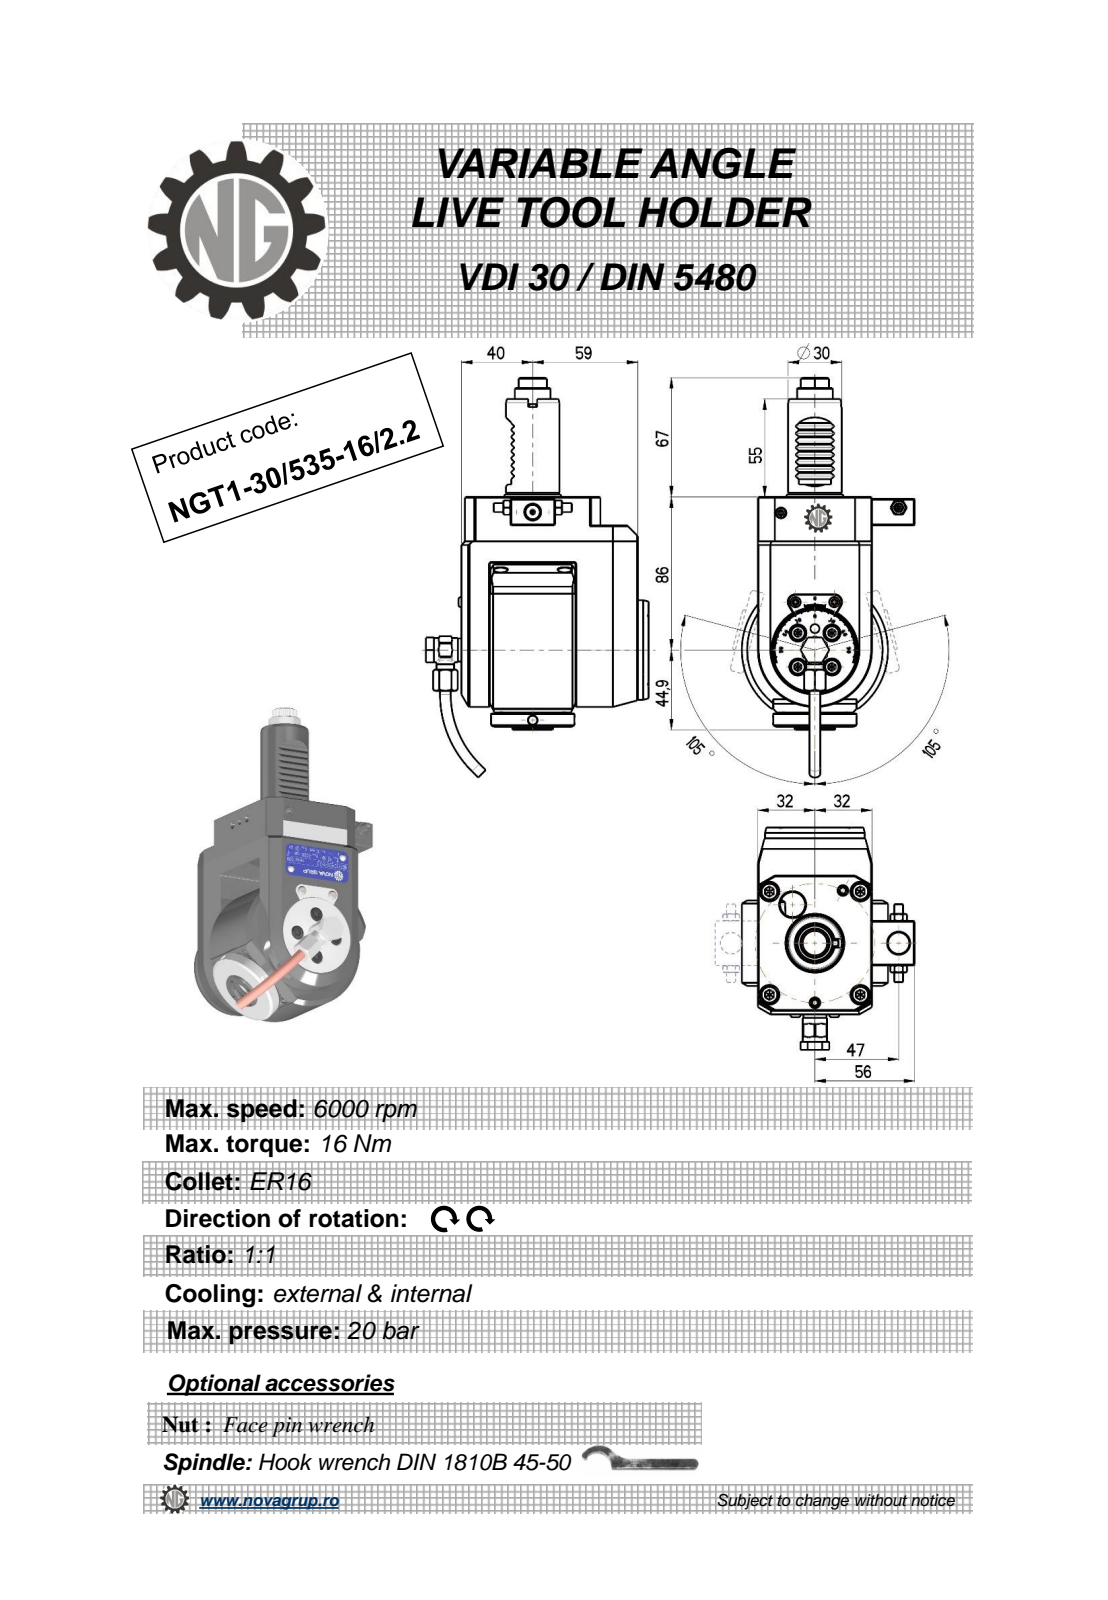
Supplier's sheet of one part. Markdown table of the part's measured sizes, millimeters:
| quantity | value |
| --- | --- |
| part name | NGT1_30_531_16_2_2 |
| STEP written by | PRO/ENGINEER BY PARAMETRIC TECHNOLOGY CORPORATION, 2010280 (CONFIG_CONTROL_DESIGN) |
| units | millimeters |
| bodies | 1 solid, 588 faces (212 planar, 209 cylindrical, 167 other) |
| overall size | 224.67 × 124.9 × 97 |
| volume | 780 866 mm³ |
| surface area | 72 475 mm² |
| round holes (diameter × count) | 3.2 × 4, 4 × 3, 5 × 2, 3 × 1, 4.2 × 1, 6.2 × 1, 9 × 1, 9.5 × 1, 11 × 1, 12 × 1, 12.5 × 1 |
| round bosses / shafts (diameter × count) | 10 × 2, 6 × 2, 5.7 × 2, 56 × 1, 47 × 1, 35 × 1, 30 × 1, 23 × 1 |
| partial cylindrical surfaces (radius × count) | 1.98 × 36, 0.26 × 12, 0.3 × 8, 0.16 × 6, 0.5 × 4, 1 × 2, 7.29 × 1, 7.7 × 1 |
| main face-to-face distances | 64, 16, 37, 99, 6, 105, 21, 14, 62, 83 |
| hole center spacings | 9.25, 13.08, 18.5, 47.9, 49.87, 50.26, 0.4, 37.75 |
